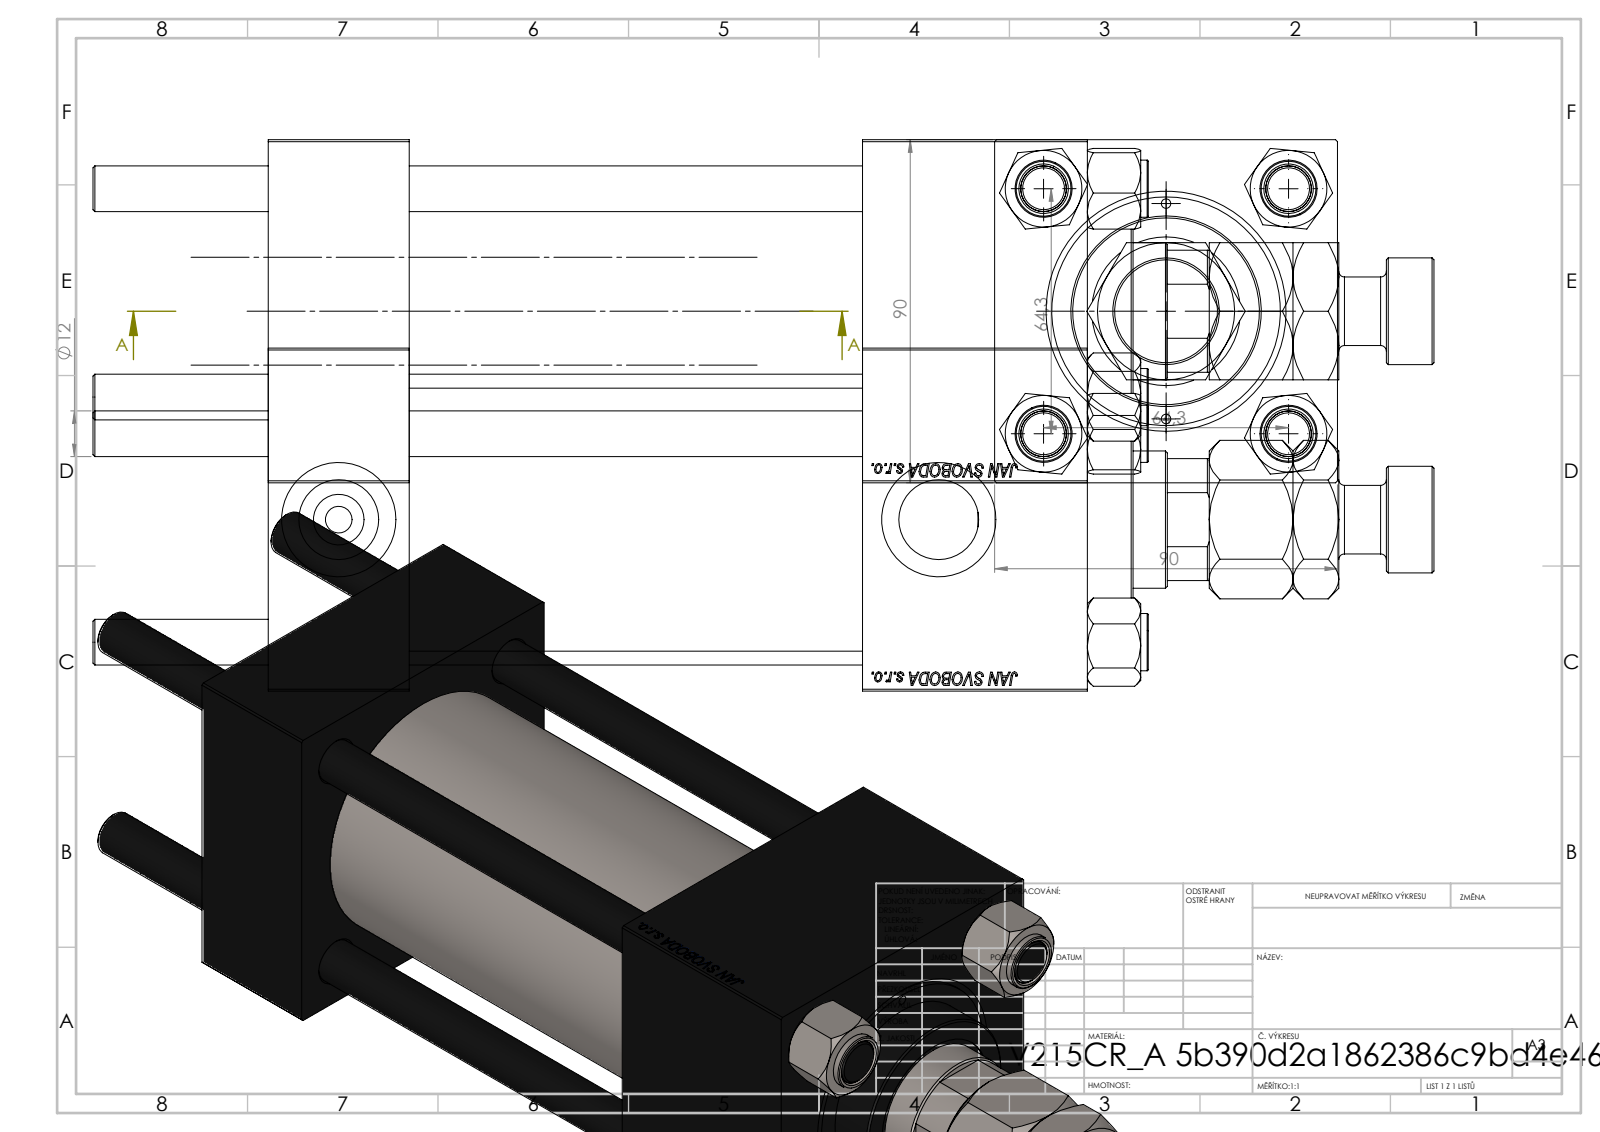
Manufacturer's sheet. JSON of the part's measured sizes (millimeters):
{"part_name": "MFA; V215CR_BODY_A; NUT_M5; CR025_012_A_0_G_A_G_M_020_+#_##_TYCINKA (+2 more)", "step_written_by": "SolidWorks 2019 (CONFIG_CONTROL_DESIGN)", "units": "millimeters", "bodies": {"solids": 12, "faces": 1192, "planar": 538, "cylindrical": 86, "other": 568}, "overall_size": [352, 90, 90], "volume_mm3": 1177000, "surface_area_mm2": 249958, "round_holes": [[12, 4], [2.5, 2], [7, 2], [20.96, 2], [30, 2], [25.5, 1], [36, 1], [39, 1], [50, 1], [60, 1], [63, 1]], "round_bosses_or_shafts": [[15, 4], [69, 1], [28, 1], [18, 1]], "partial_cylinders_radius": [[17.5, 1]], "face_to_face_distances": [90, 37, 215, 178, 59, 156, 119, 186.3, 149.3, 30.3], "hole_center_spacings": [32.39, 45.47, 64.3, 68.42, 28.25, 90.93, 56.5, 157.5]}
